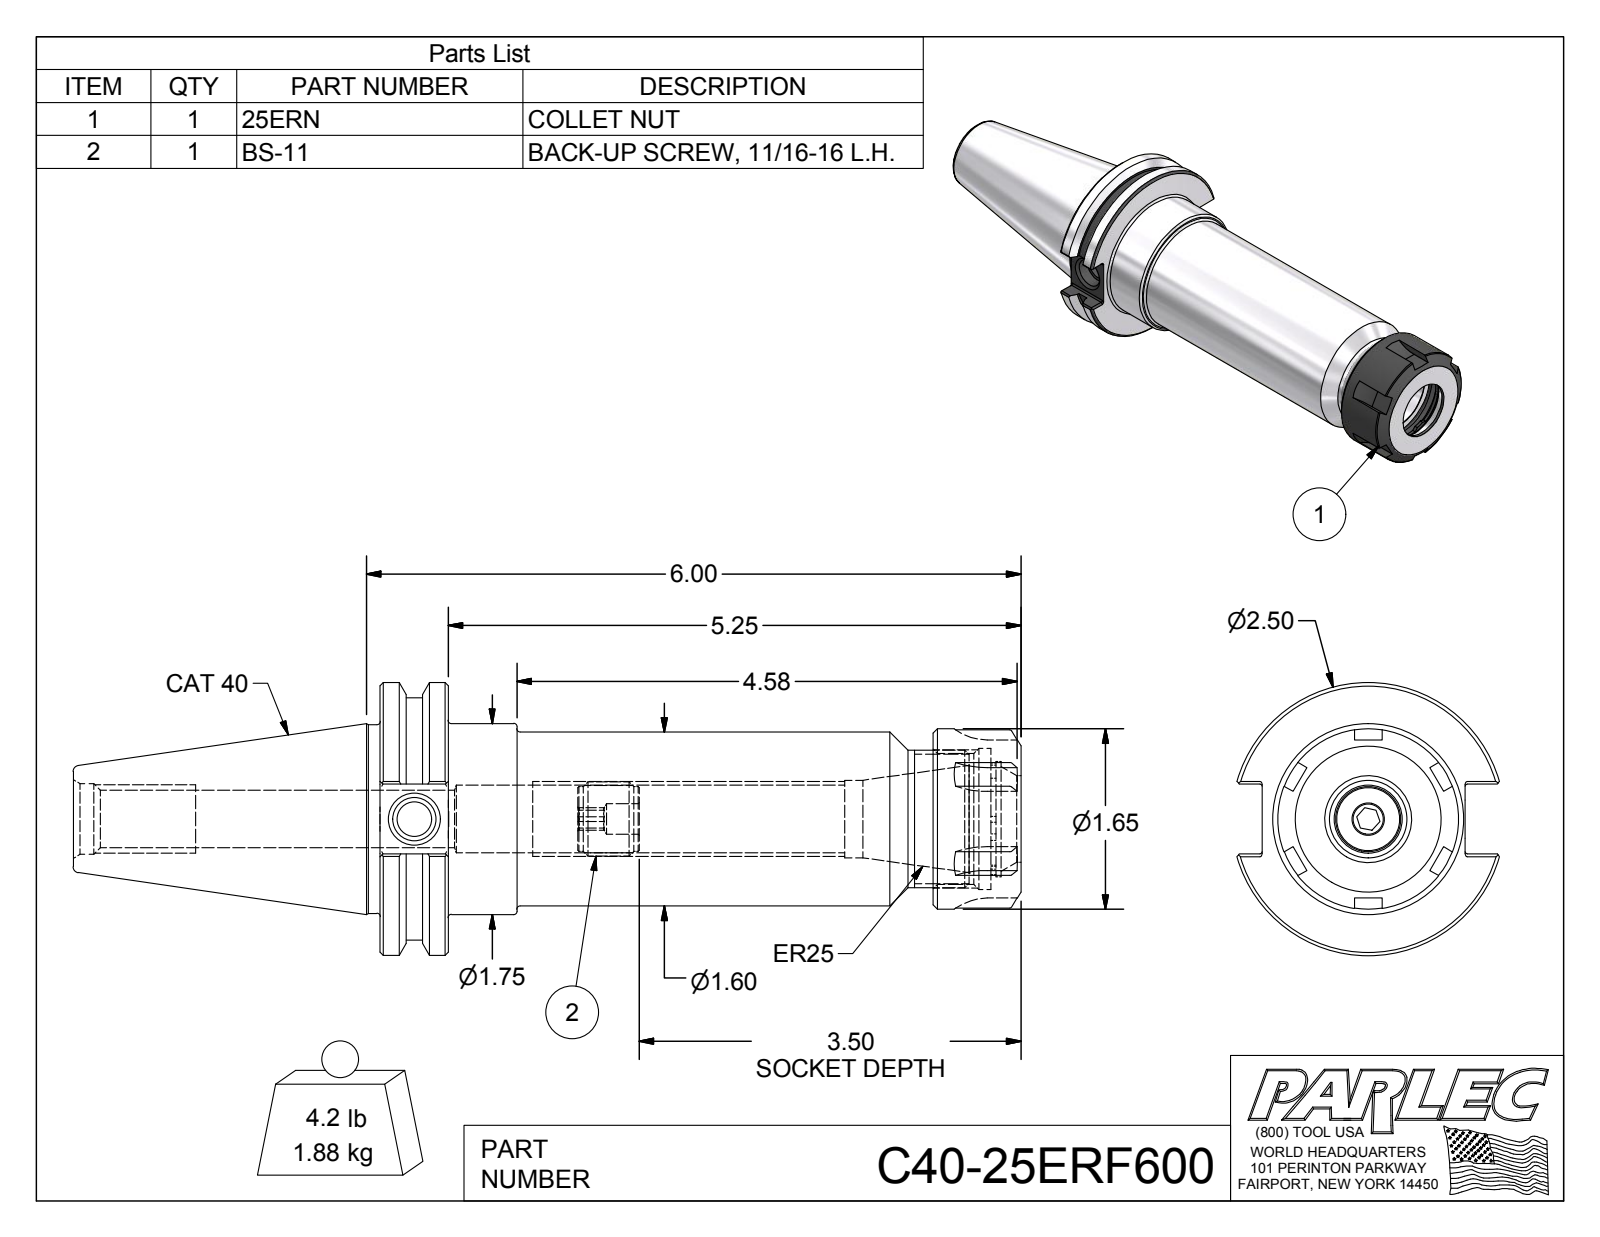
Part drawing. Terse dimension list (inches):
name: C40-25ER6-1; 25ERN; BS-11; C40-25ERF600
written by: Autodesk Inventor 2016 (AUTOMOTIVE_DESIGN)
unit: in
bodies: 3 solids, 187 faces (76 planar, 51 cylindrical, 60 other)
size: 8.687 × 2.5 × 2.404
volume: 14.7 in³; area: 76.26 in²
holes: 1× ⌀0.28, 1× ⌀0.315, 1× ⌀0.399, 1× ⌀0.527, 1× ⌀0.62, 1× ⌀0.648, 1× ⌀0.71, 1× ⌀0.8, 1× ⌀1.201, 1× ⌀1.294
bosses: 1× ⌀2.5, 1× ⌀2.219, 1× ⌀1.75, 1× ⌀1.73, 1× ⌀1.654, 1× ⌀1.595, 1× ⌀1.26, 1× ⌀0.681
rounds: 24× R0.02, 1× R0.472, 1× R0.514, 1× R0.529
face distances: 0.625, 5.875, 5.25, 5.065, 4.44, 0.81, 5.596, 4.97, 0.53, 0.28
